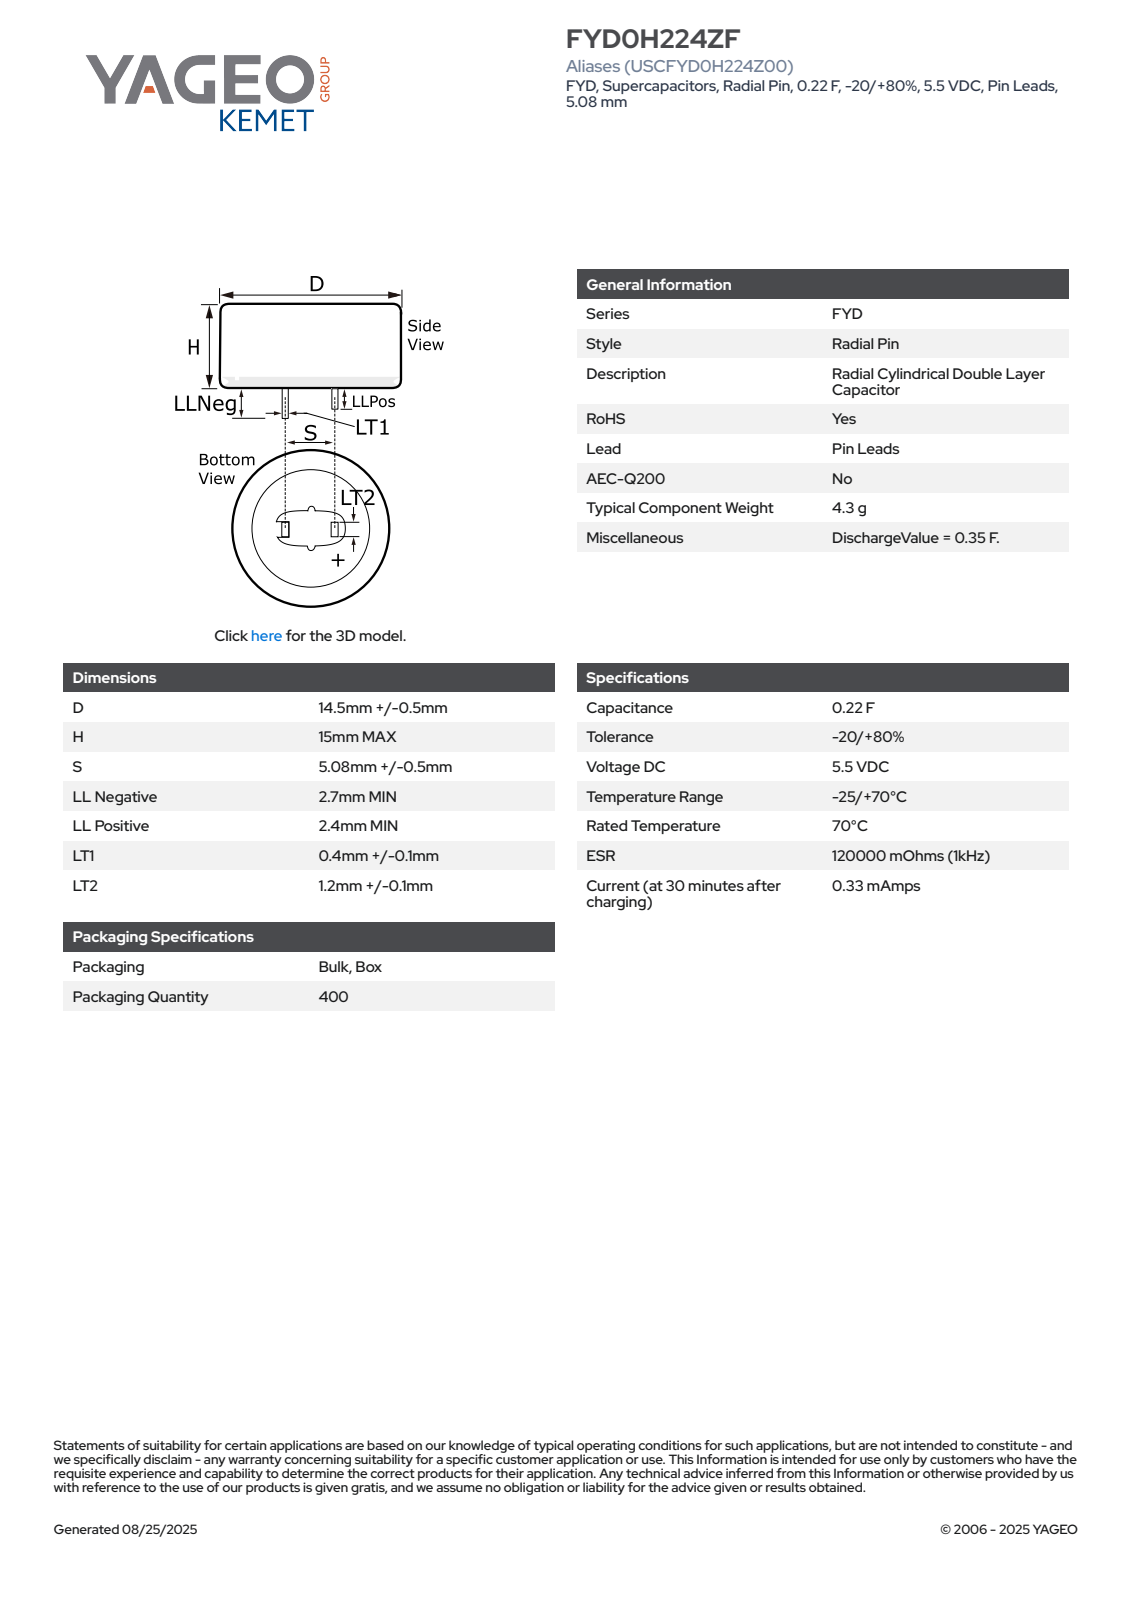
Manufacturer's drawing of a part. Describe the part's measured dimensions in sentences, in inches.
The part is named "CDR_LPLLN_D15L15S5.08LLNEG2.7LLPOS2.4LT10.5LT21.3". Its 3-D file was written by "SolidWorks 2014 (AUTOMOTIVE_DESIGN)". It is 1 solid with 78 faces: 70 planar, 4 cylindrical and 4 other. Overall it measures 0.697 by 0.591 by 0.591 inches. Its volume is 0.161 cubic inches and its surface area 1.61 square inches. Round bosses or shafts: 1 of diameter 0.591. Partial cylindrical surfaces (rounded edges, fillets, slot ends): 1 of radius 0.296. The main face-to-face distances are 0.591, 0.59, 0.02, 0.2, 0.22, 0.18, 0.051, 0.106, 0.696, 0.697.
